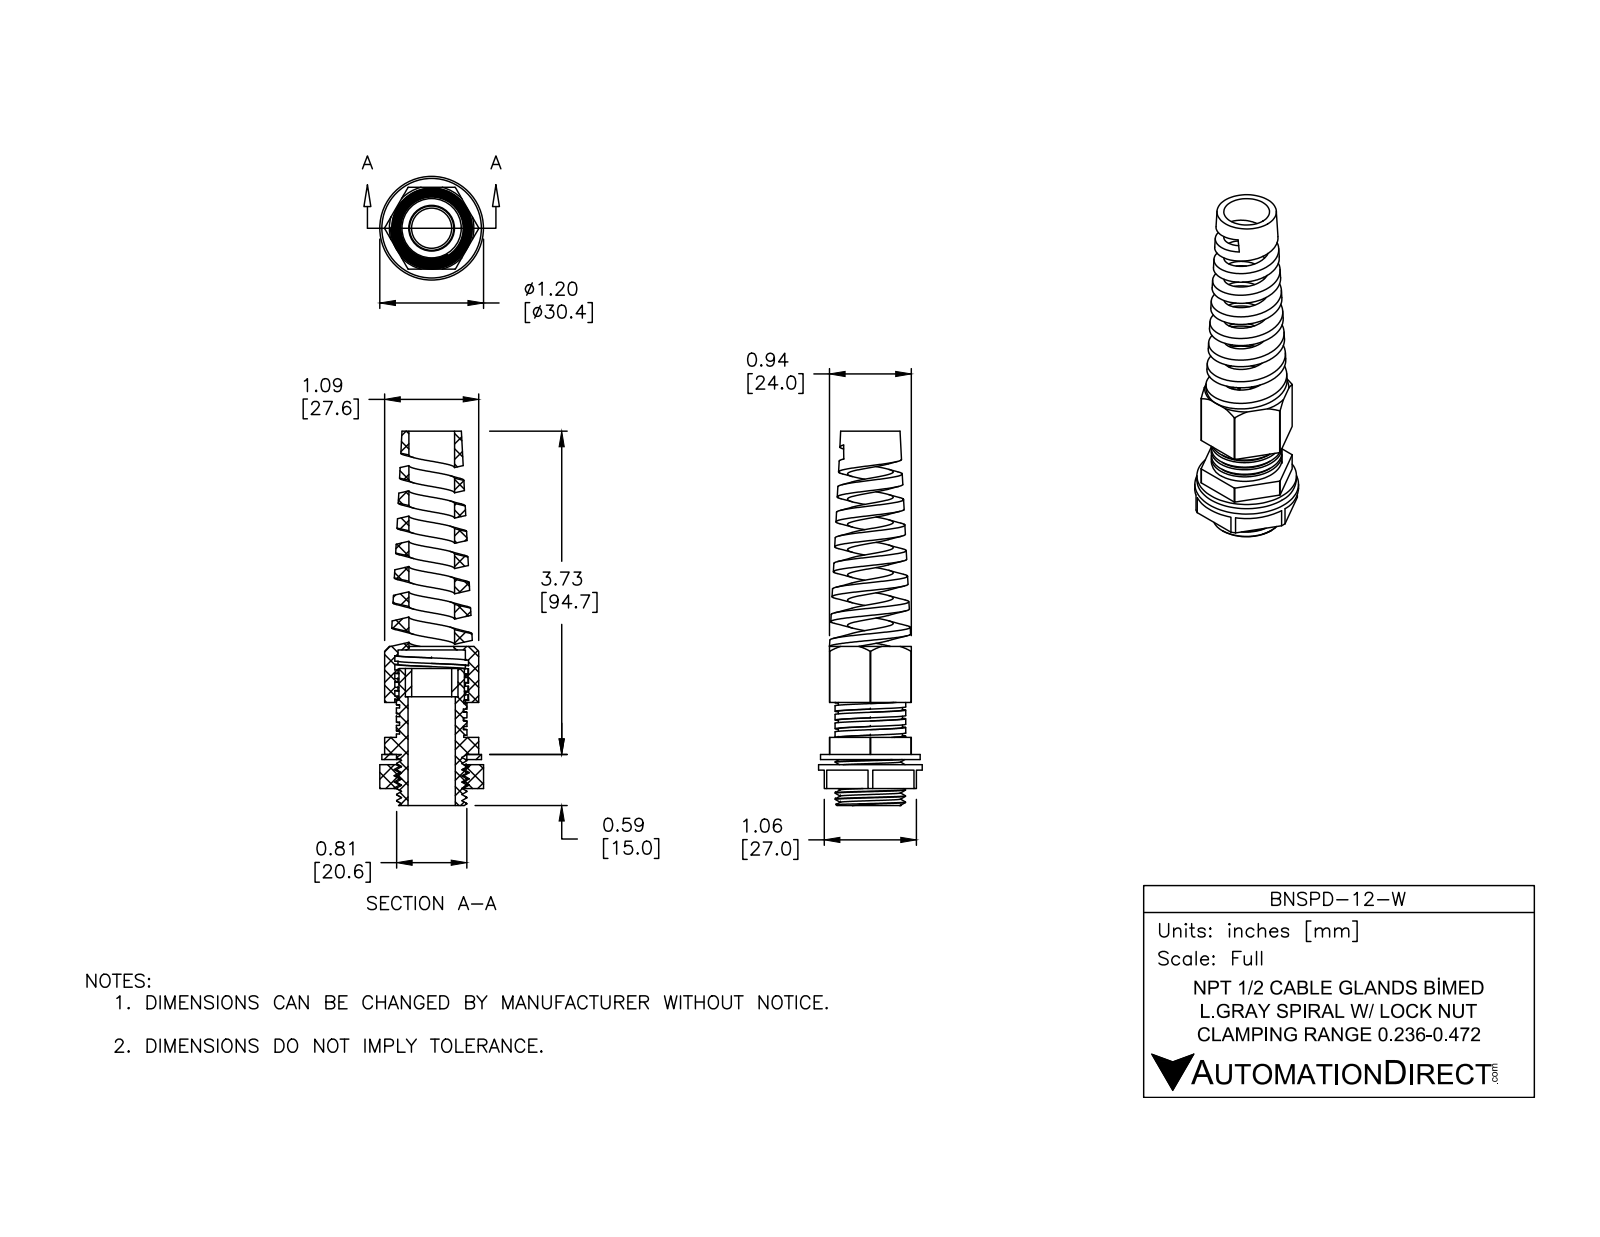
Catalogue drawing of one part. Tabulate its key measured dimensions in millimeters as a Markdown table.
| quantity | value |
| --- | --- |
| part name | BNSPBX-12-W |
| STEP written by | SolidWorks 2015 (CONFIG_CONTROL_DESIGN) |
| units | millimeters |
| bodies | 5 solids, 239 faces (105 planar, 96 cylindrical, 38 other) |
| overall size | 109.73 × 30.4 × 30.4 |
| volume | 18 629 mm³ |
| surface area | 20 985 mm² |
| round holes (diameter × count) | 11.74 × 1, 13.4 × 1, 13.87 × 1, 15.4 × 1, 19.12 × 1, 19.77 × 1, 20.6 × 1 |
| round bosses / shafts (diameter × count) | 30.4 × 1, 29.2 × 1, 20.7 × 1, 20.57 × 1, 19.2 × 1 |
| partial cylindrical surfaces (radius × count) | 13.79 × 1 |
| main face-to-face distances | 23.98, 1.5, 1.51, 25.49, 3, 7, 8.5, 10, 27, 41.64 |
